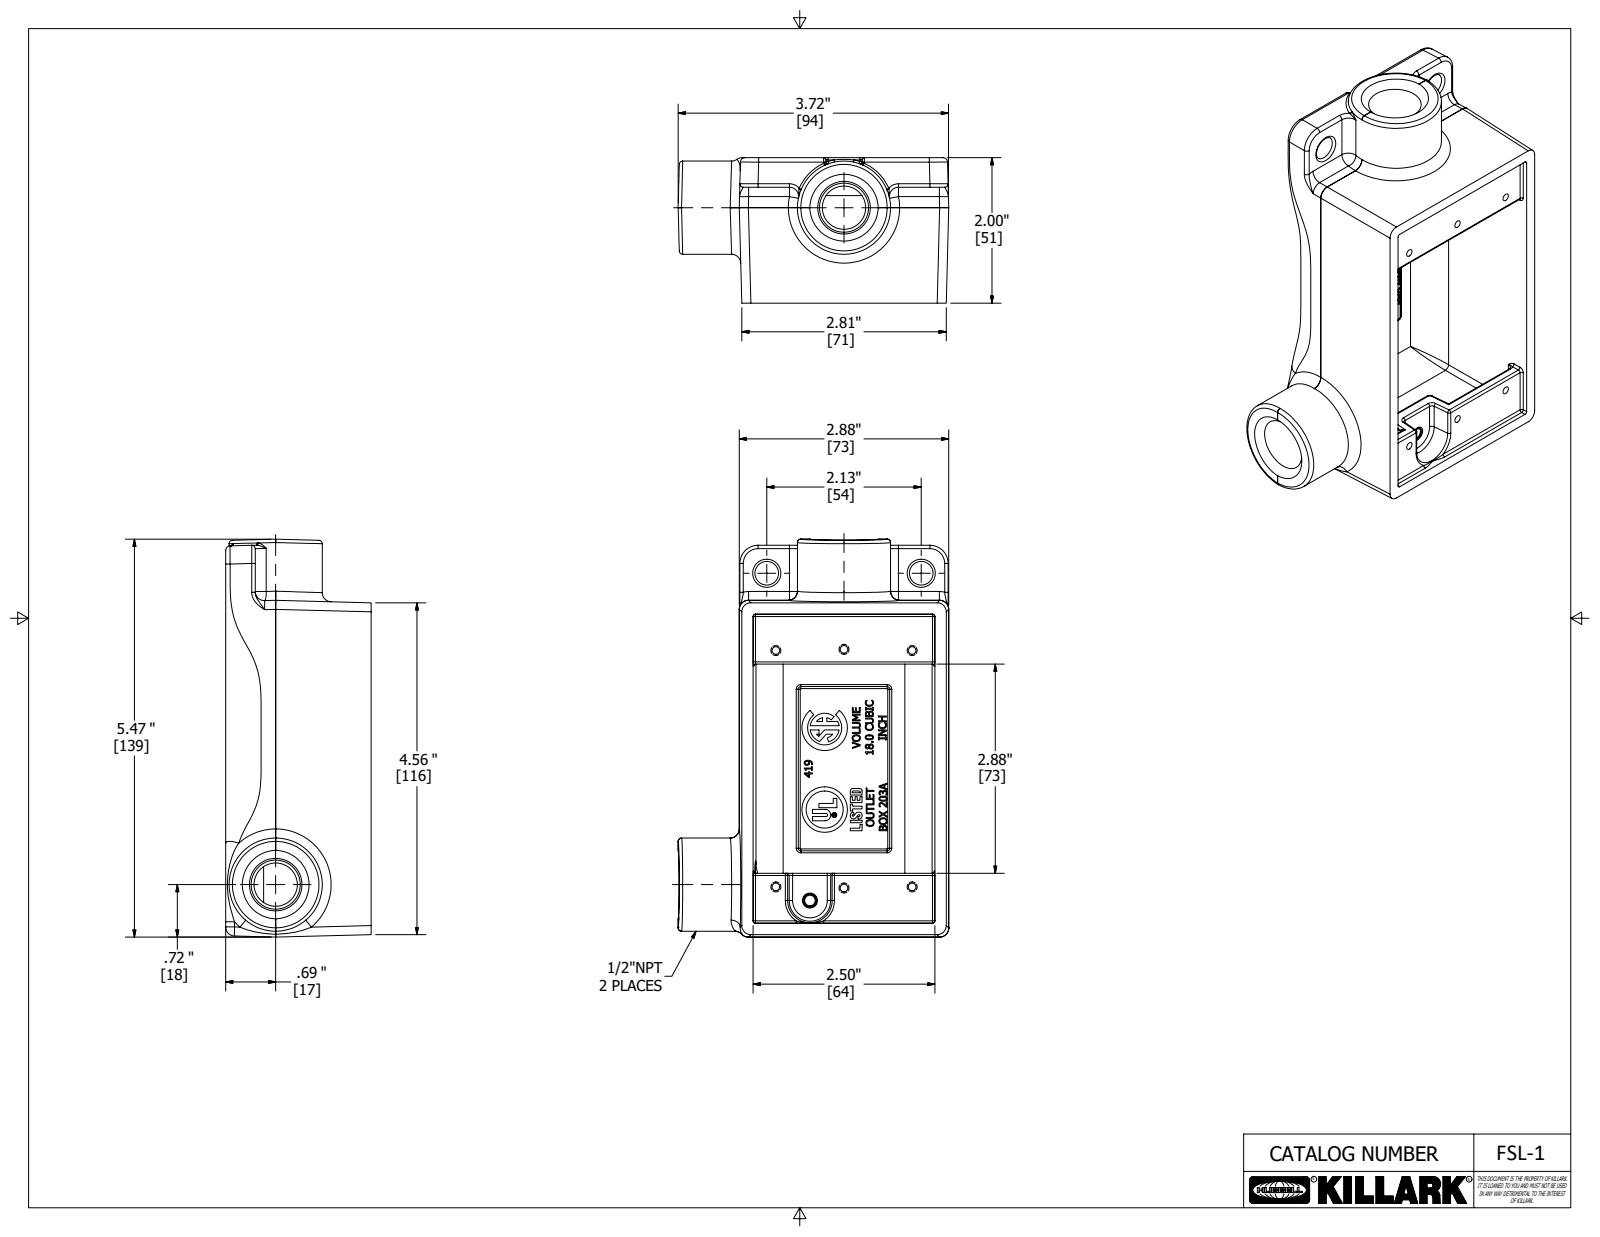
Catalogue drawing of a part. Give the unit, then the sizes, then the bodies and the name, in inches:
Units: inches
Overall size (bounding box): 5.472 × 3.722 × 2.075
Round holes (diameter × count): ⌀0.104 ×6, ⌀0.595 ×2, ⌀0.069 ×1, ⌀0.145 ×1, ⌀0.625 ×1
Round bosses / shafts (diameter × count): ⌀1.281 ×1, ⌀0.509 ×1, ⌀0.058 ×1
Partial cylindrical surfaces — rounded edges, fillets, slot ends (radius × count): R0.031 ×56, R0.125 ×11, R0.047 ×7, R0.094 ×7, R0.062 ×5, R0.375 ×4, R0.013 ×2, R0.014 ×2
Main face-to-face distances: 2.656, 0.156, 4.406, 1.75, 0.225, 0.031, 1.719, 1.594, 1.906, 0.25
Hole centre spacings: 0.937, 3.397, 1.875, 3.25, 3.752, 0.153, 0.5, 0.505
Volume: 9.777 in³ · Surface area: 95.4 in²
Bodies: 1 solid, 1161 faces (566 planar, 172 cylindrical, 423 other)
Part name (STEP PRODUCT): 23857-3
STEP written by: Autodesk Inventor 2020 (AUTOMOTIVE_DESIGN)
